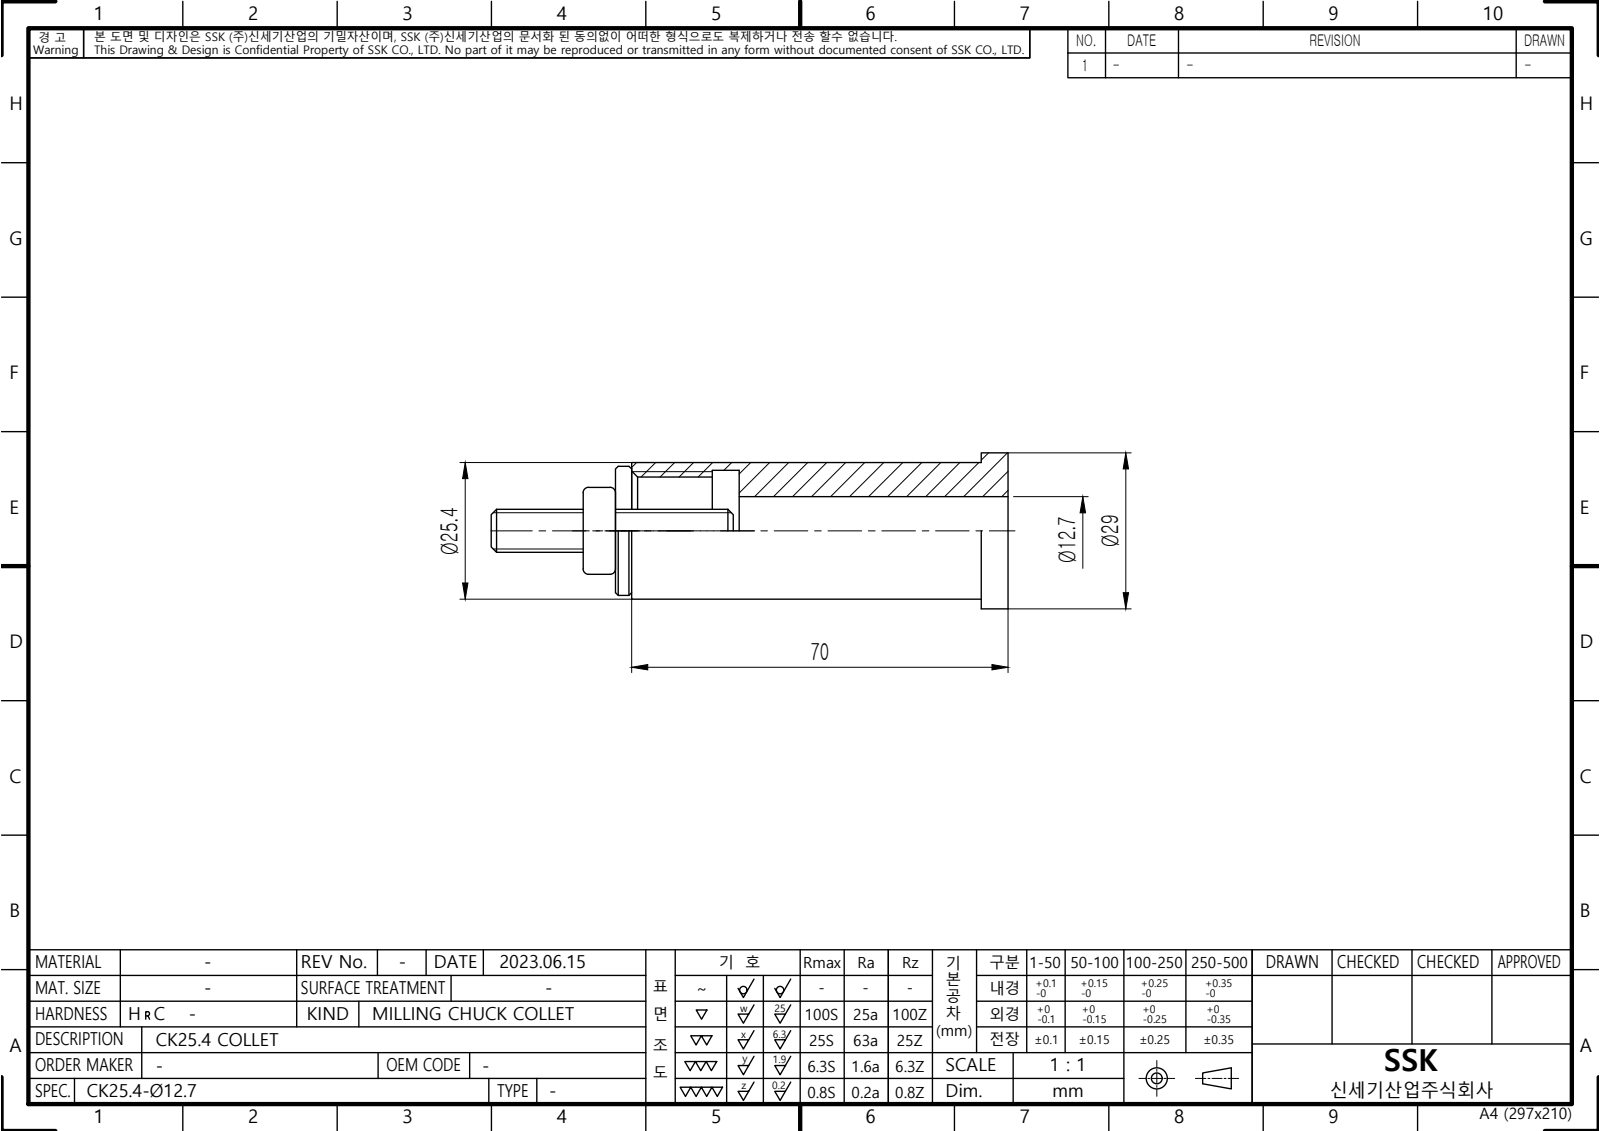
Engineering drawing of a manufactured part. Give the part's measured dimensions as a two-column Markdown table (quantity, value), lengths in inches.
| quantity | value |
| --- | --- |
| part name | LO-CK19.05-12.7 |
| STEP written by | Autodesk Inventor 2022 (AUTOMOTIVE_DESIGN) |
| units | inches |
| bodies | 1 solid, 10 faces (5 planar, 5 cylindrical, 0 other) |
| overall size | 2.756 × 1.142 × 1.142 |
| volume | 1.389 in³ |
| surface area | 15.74 in² |
| round holes (diameter × count) | 0.5 × 1, 0.824 × 1, 0.886 × 1 |
| round bosses / shafts (diameter × count) | 1.142 × 1, 1 × 1 |
| main face-to-face distances | 1.969, 0.197, 0.787, 2.756, 2.559, 1.772, 0.591, 2.165 |
